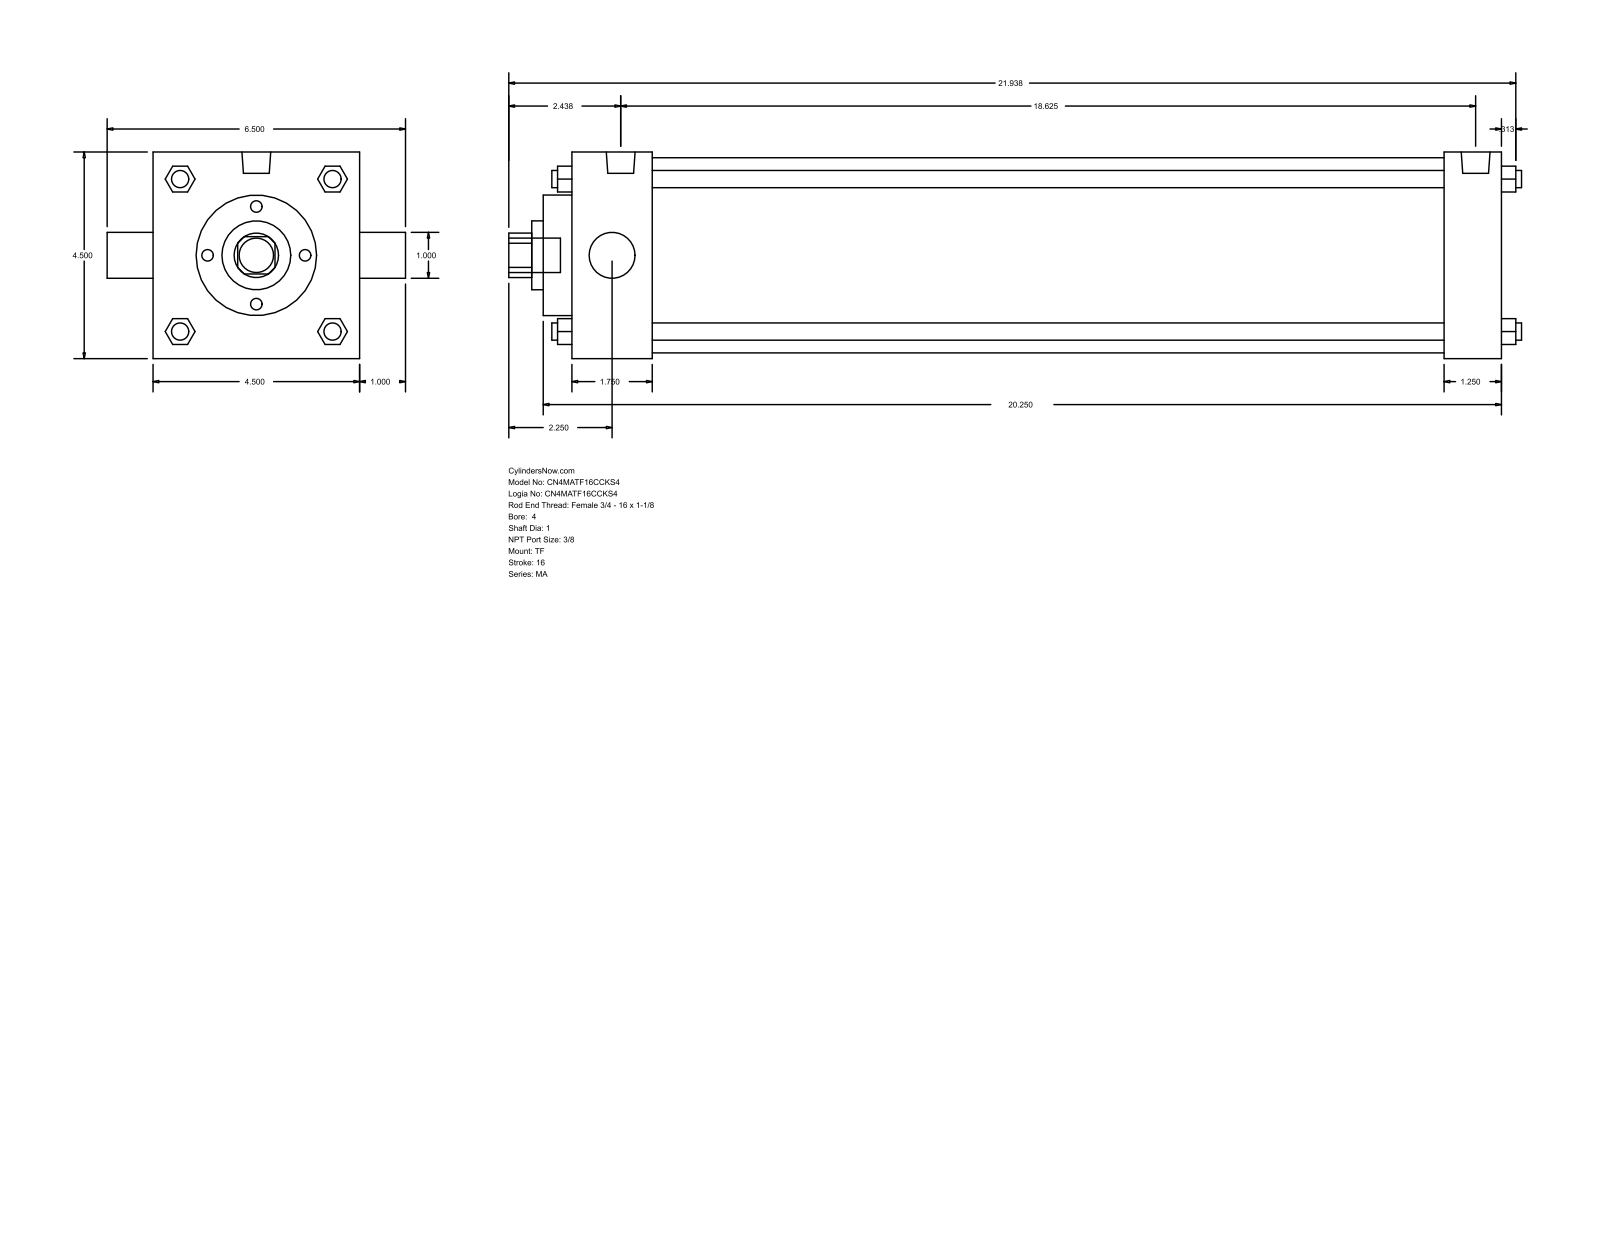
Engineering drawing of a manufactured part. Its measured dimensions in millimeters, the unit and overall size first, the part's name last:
Units: millimetres
Overall size (bounding box): 560.39 × 165.1 × 114.3
Round holes (diameter × count): ⌀25.4 ×2, ⌀38.1 ×1, ⌀66.67 ×1, ⌀107.95 ×1
Round bosses / shafts (diameter × count): ⌀9.53 ×4, ⌀11.11 ×3, ⌀15.93 ×2, ⌀19.05 ×1
Partial cylindrical surfaces — rounded edges, fillets, slot ends (radius × count): R12.29 ×1
Main face-to-face distances: 114.3, 514.35, 482.6, 31.75, 44.46, 438.14, 469.89, 530.22, 15.87, 60.33
Bodies: 0 solids, 122 faces (93 planar, 29 cylindrical, 0 other)
Part name (STEP PRODUCT): MA_TF__0400_1
STEP written by: GSSL Pune (CONFIG_CONTROL_DESIGN)
